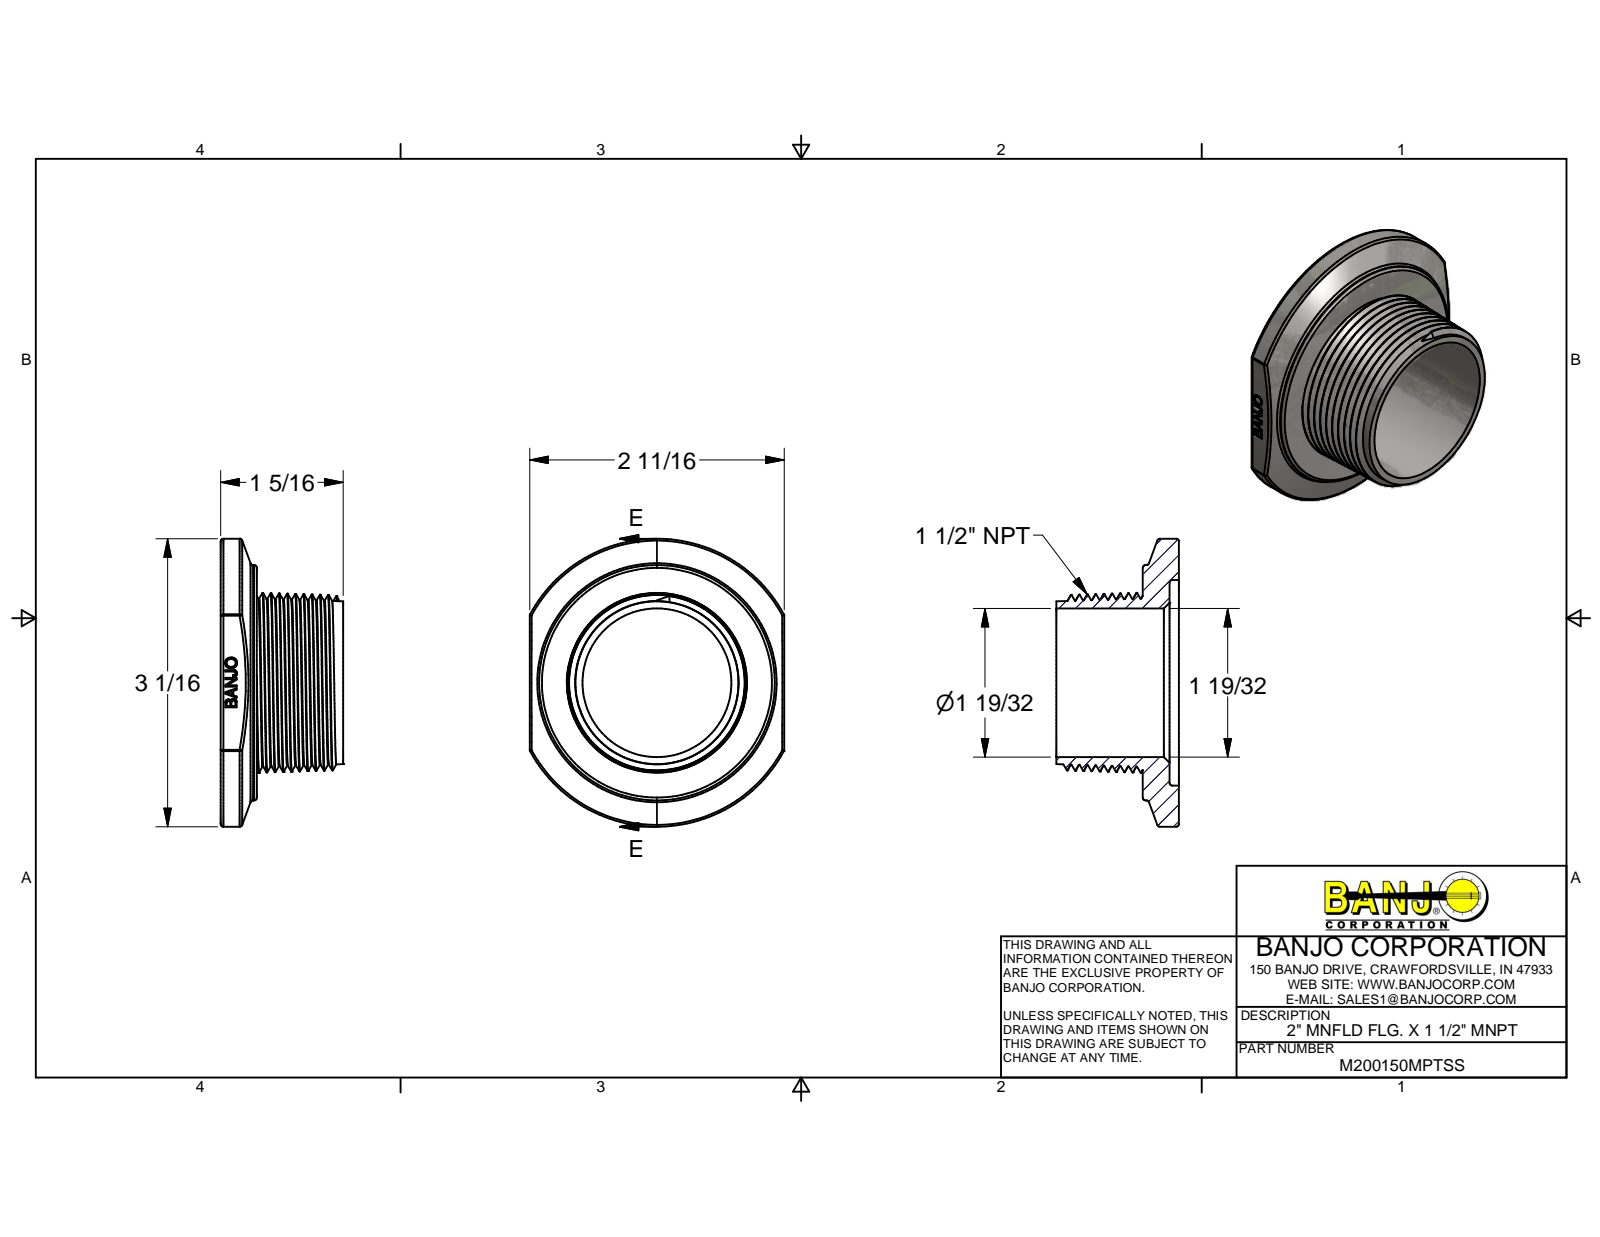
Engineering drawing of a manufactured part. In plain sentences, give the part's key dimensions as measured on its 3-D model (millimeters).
The part is named "M200150MPTSS". Its 3-D file was written by "Autodesk Inventor 2013 (AUTOMOTIVE_DESIGN)". It is 1 solid with 318 faces: 141 planar, 11 cylindrical and 166 other. Overall it measures 77.7 by 68.6 by 33 millimeters. Its volume is 34 270 cubic millimeters and its surface area 18 210 square millimeters. Round holes: 1 of diameter 40.1, 1 of diameter 55.5. Round bosses or shafts: 1 of diameter 63.5. Partial cylindrical surfaces (rounded edges, fillets, slot ends): 6 of radius 0.8, 1 of radius 38.9. The main face-to-face distances are 9.8, 7.2, 2.5, 23.3, 30.5, 33, 68.6, 0.8, 67.8, 67.1.
